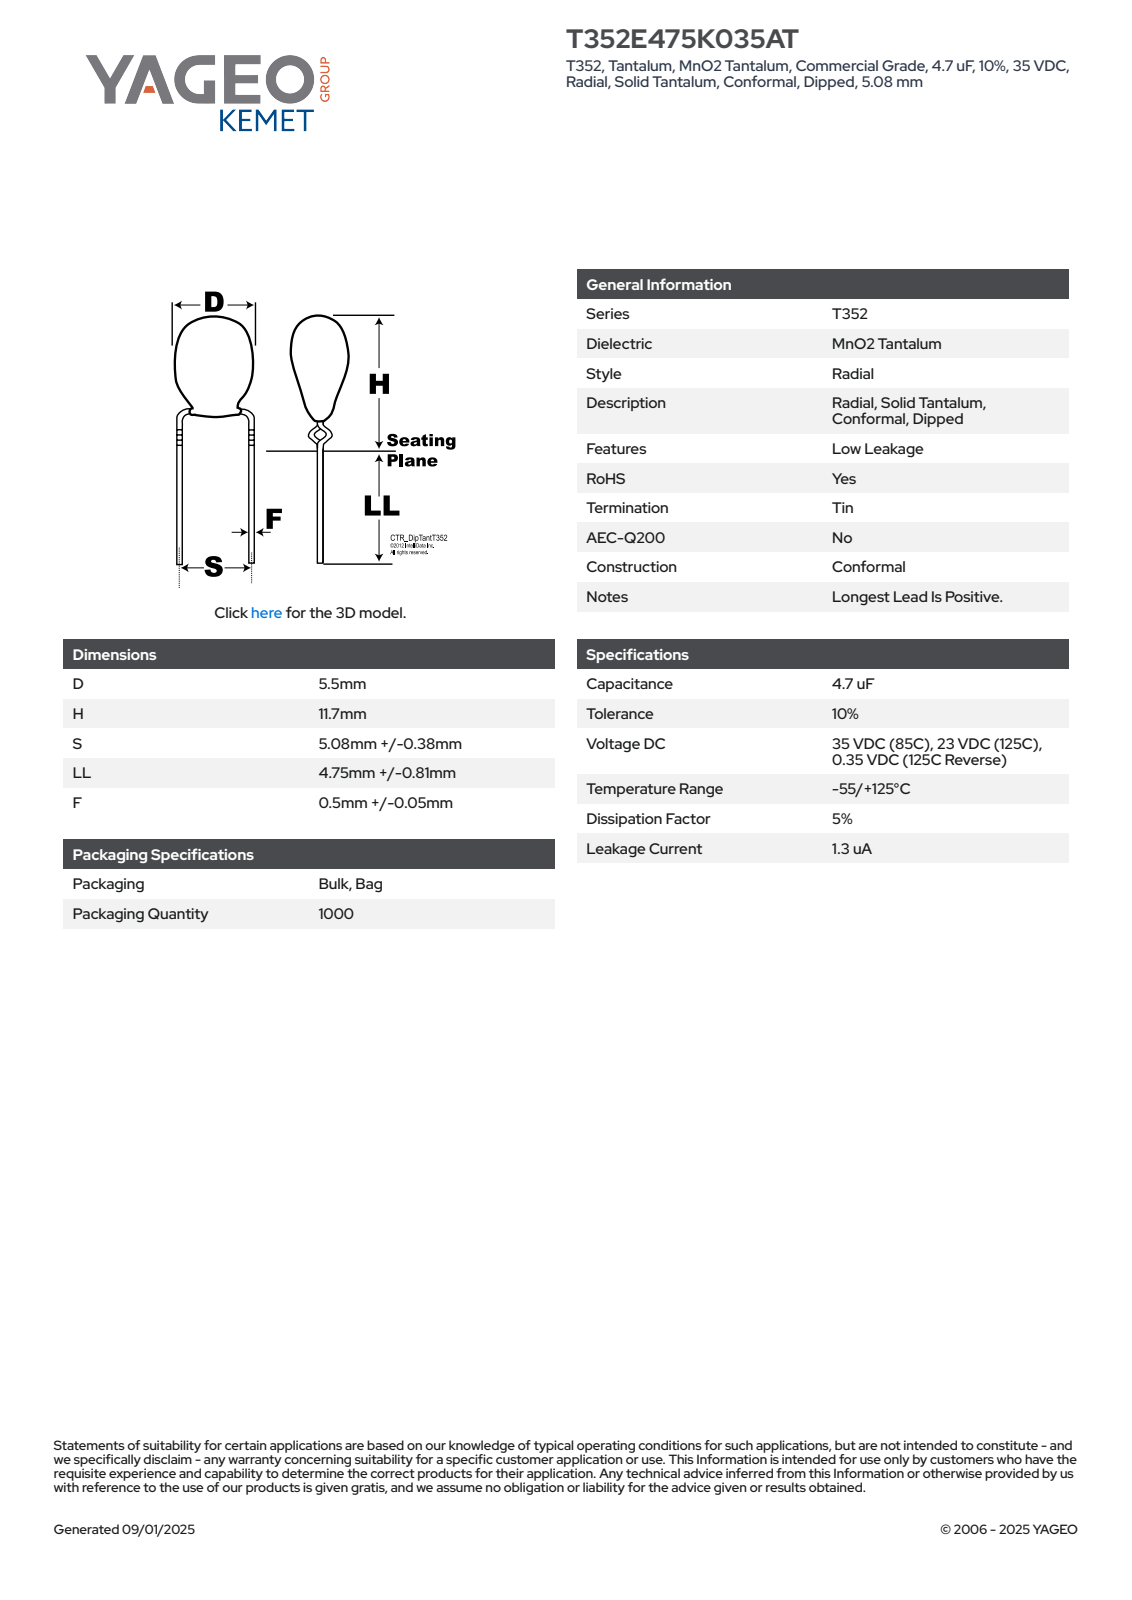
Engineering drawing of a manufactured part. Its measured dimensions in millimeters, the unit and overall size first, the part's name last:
Units: millimetres
Overall size (bounding box): 17.26 × 5.63 × 5.5
Round bosses / shafts (diameter × count): ⌀0.55 ×2, ⌀5.5 ×1
Partial cylindrical surfaces — rounded edges, fillets, slot ends (radius × count): R2.74 ×1
Main face-to-face distances: 9.18, 4.41, 4.77, 3.8, 0.61, 5.38, 0.49, 3.92, 5.26, 4.18
Volume: 197 mm³ · Surface area: 210 mm²
Bodies: 1 solid, 92 faces (26 planar, 10 cylindrical, 56 other)
Part name (STEP PRODUCT): CTR_T352_D5.5H11.7S5.08LL5.56F0.55
STEP written by: SolidWorks 2014 (AUTOMOTIVE_DESIGN)
